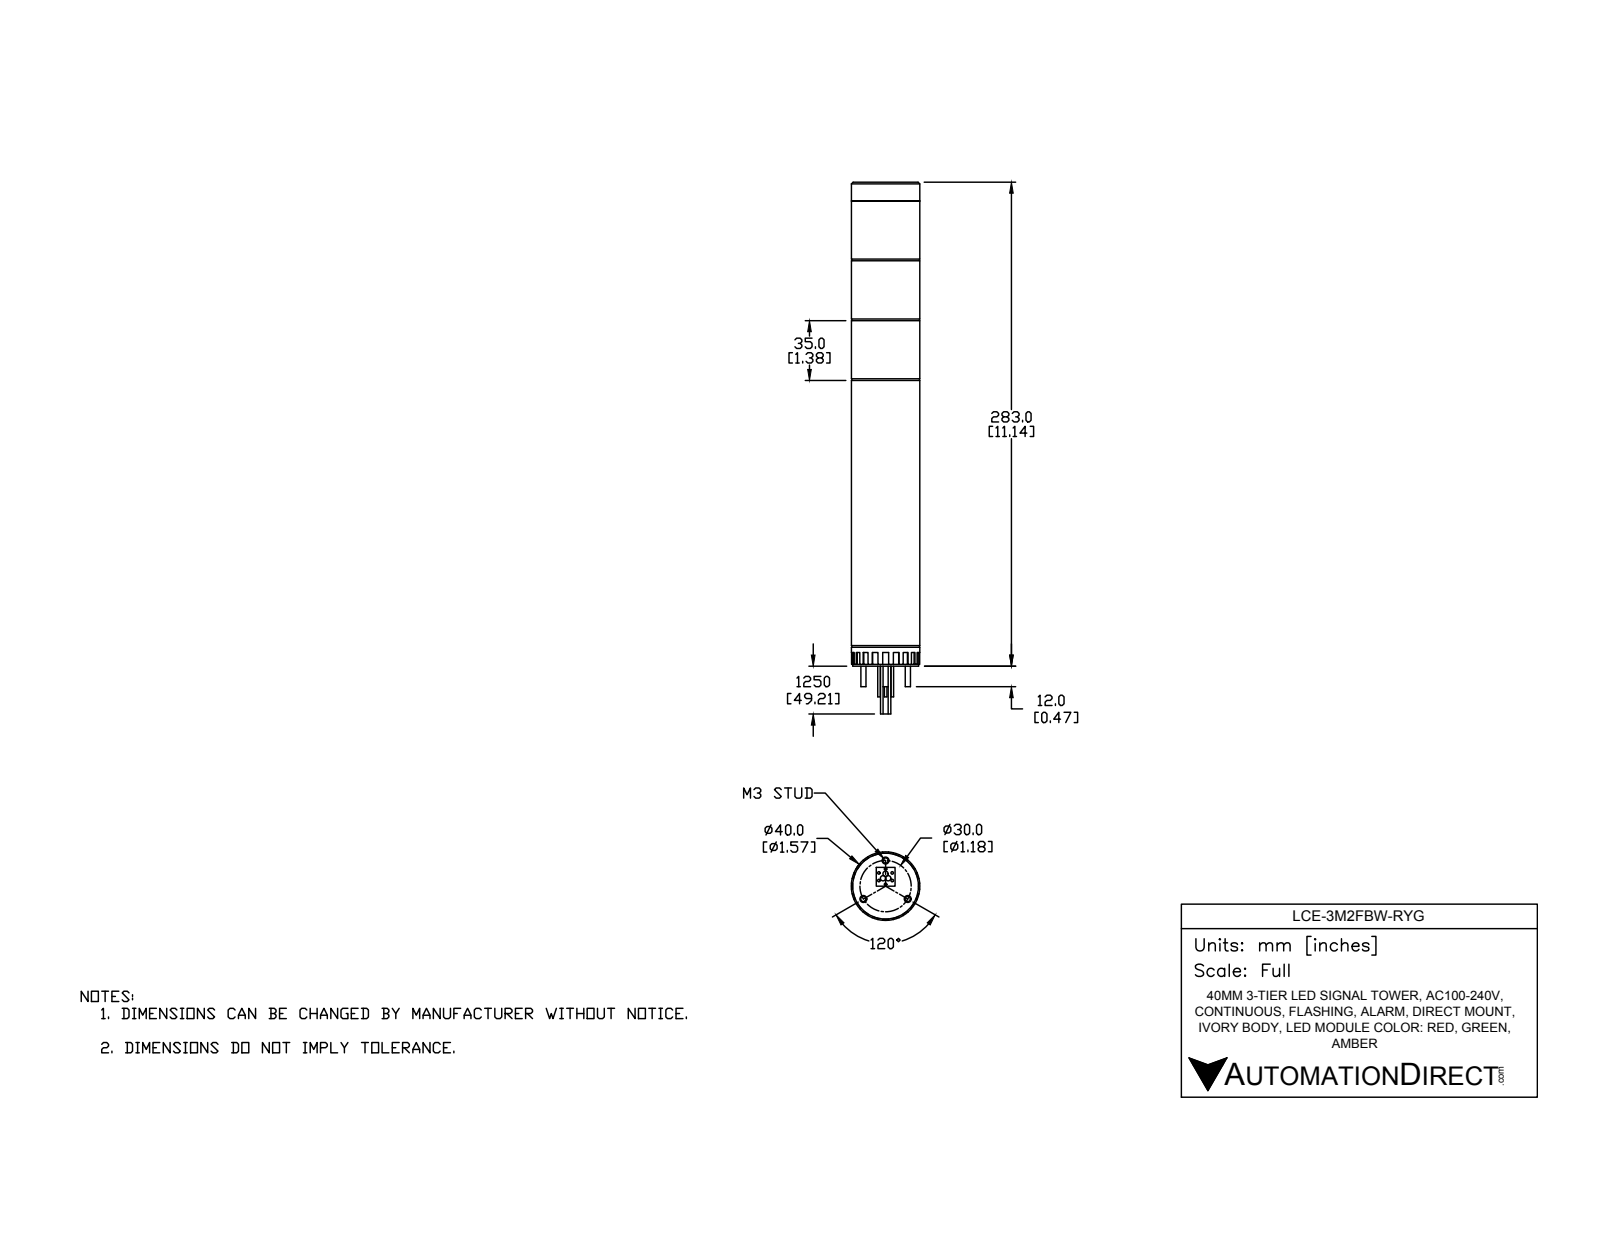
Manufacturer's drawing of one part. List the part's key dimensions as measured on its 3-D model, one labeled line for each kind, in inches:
Part name (STEP PRODUCT): LCE-3M2FBW-RYG
STEP written by: SolidWorks 2016 (AUTOMOTIVE_DESIGN)
Units: inches
Bodies: 28 solids, 230 faces (162 planar, 64 cylindrical, 4 other)
Overall size (bounding box): 12.244 × 1.575 × 1.575
Volume: 21.65 in³ · Surface area: 101.7 in²
Round holes (diameter × count): ⌀0.157 ×3, ⌀0.315 ×1
Round bosses / shafts (diameter × count): ⌀0.059 ×10, ⌀0.118 ×3, ⌀0.098 ×3, ⌀1.575 ×1, ⌀1.555 ×1, ⌀1.516 ×1, ⌀0.217 ×1
Main face-to-face distances: 1.378, 0.039, 2.756, 1.339, 1.417, 2.717, 6.142, 7.52, 8.898, 0.433
Hole centre spacings: 0.591, 1.023
